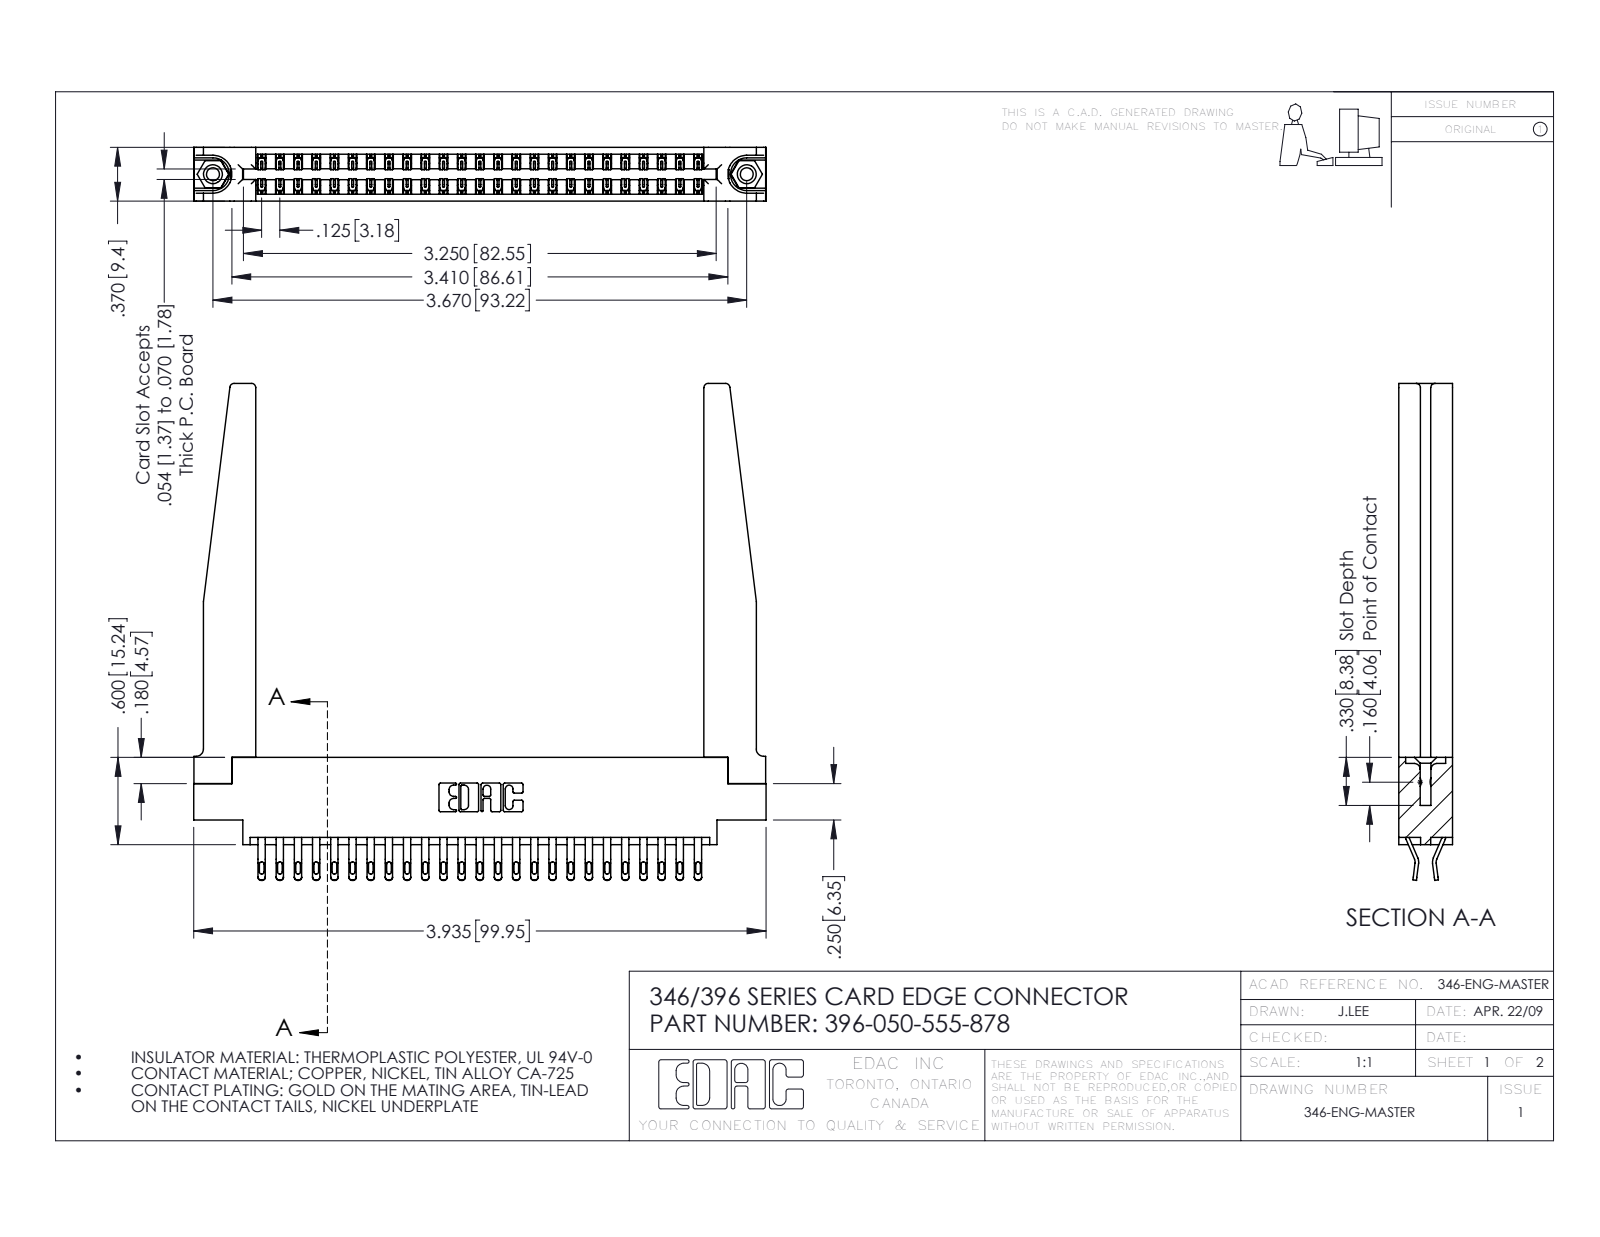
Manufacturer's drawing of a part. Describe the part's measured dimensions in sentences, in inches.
The part is named "346-220-078_345-220-078; 345-292-001_555 Tail; 346 Part_0.170 Offset - 0.156 Dia-TH; 396-050-555-878 (+1 more)". Its 3-D file was written by "SolidWorks 2016 (CONFIG_CONTROL_DESIGN)". It is 55 solids with 3260 faces: 1872 planar, 1336 cylindrical and 52 other. Overall it measures 3.935 by 3.415 by 0.37 inches. Its volume is 1.008 cubic inches and its surface area 31.26 square inches. Round holes: 2 of diameter 0.089, 2 of diameter 0.125, 2 of diameter 0.156, 1 of diameter 0.064. Round bosses or shafts: 2 of diameter 0.155. Partial cylindrical surfaces (rounded edges, fillets, slot ends): 100 of radius 0.016, 100 of radius 0.02, 75 of radius 0.006, 22 of radius 0.01, 8 of radius 0.03, 6 of radius 0.007, 6 of radius 0.031, 4 of radius 0.05. The main face-to-face distances are 0.37, 0.048, 0.322, 0.072, 0.148, 0.15, 0.25, 0.025, 0.298, 0.275. The hole center spacings are 0.246, 3.462, 3.67.
